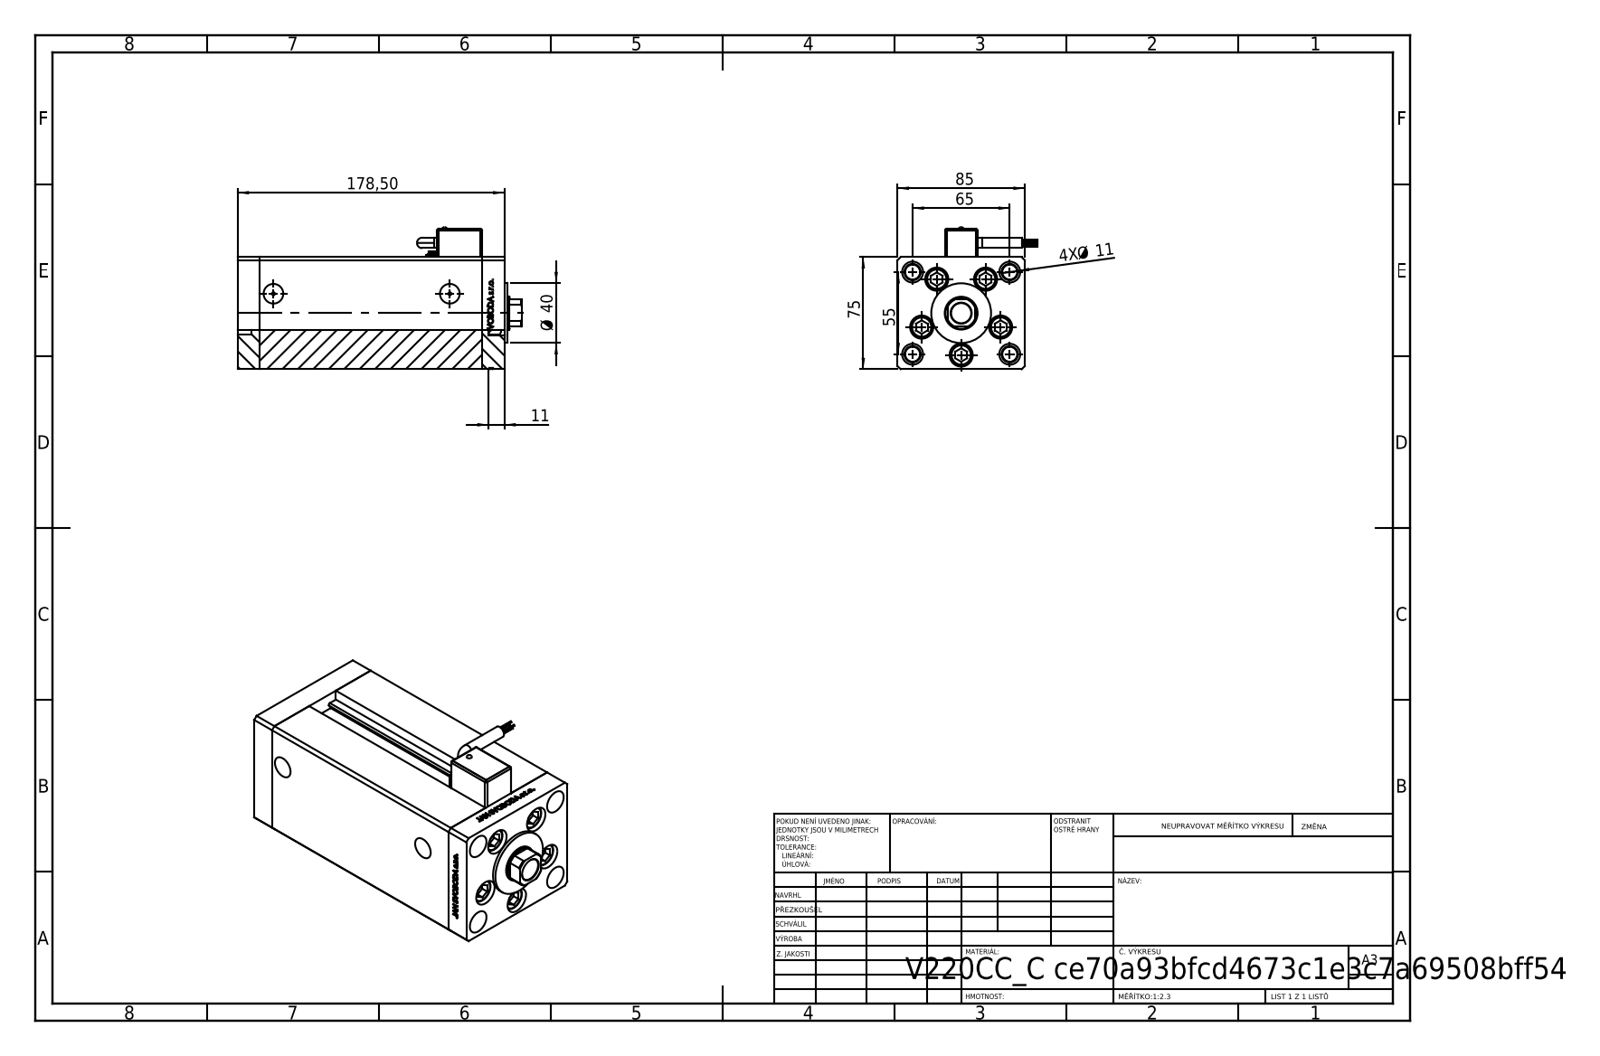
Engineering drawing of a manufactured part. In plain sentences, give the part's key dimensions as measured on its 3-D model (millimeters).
The part is named "ALLEN BOLT; V220C FRONT; V220C_C MIDDLE; V220C_VC_C (+2 more)". Its 3-D file was written by "SolidWorks 2019 (CONFIG_CONTROL_DESIGN)". It is 14 solids with 1273 faces: 581 planar, 212 cylindrical and 480 other. Overall it measures 190 by 95.1 by 93.3 millimeters. Its volume is 964 221 cubic millimeters and its surface area 186 156 square millimeters. Round holes: 9 of diameter 11, 5 of diameter 15.5, 4 of diameter 10, 4 of diameter 14, 2 of diameter 2, 2 of diameter 13.16, 1 of diameter 3.6, 1 of diameter 5, 1 of diameter 7, 1 of diameter 13.5, 1 of diameter 14.5, 1 of diameter 22. Round bosses or shafts: 5 of diameter 8, 4 of diameter 14.5, 4 of diameter 0.85, 2 of diameter 7, 1 of diameter 40, 1 of diameter 6, 1 of diameter 3.5, 1 of diameter 2.5. Partial cylindrical surfaces (rounded edges, fillets, slot ends): 14 of radius 1, 2 of radius 0.93, 2 of radius 4, 1 of radius 10.5. The main face-to-face distances are 85, 75, 15, 148.5, 163.5, 10.5, 178.5, 34.25, 68.5, 144.25. The hole center spacings are 28, 42.57, 16.86, 19.17, 32.33, 32.5, 33.63, 37.33.
